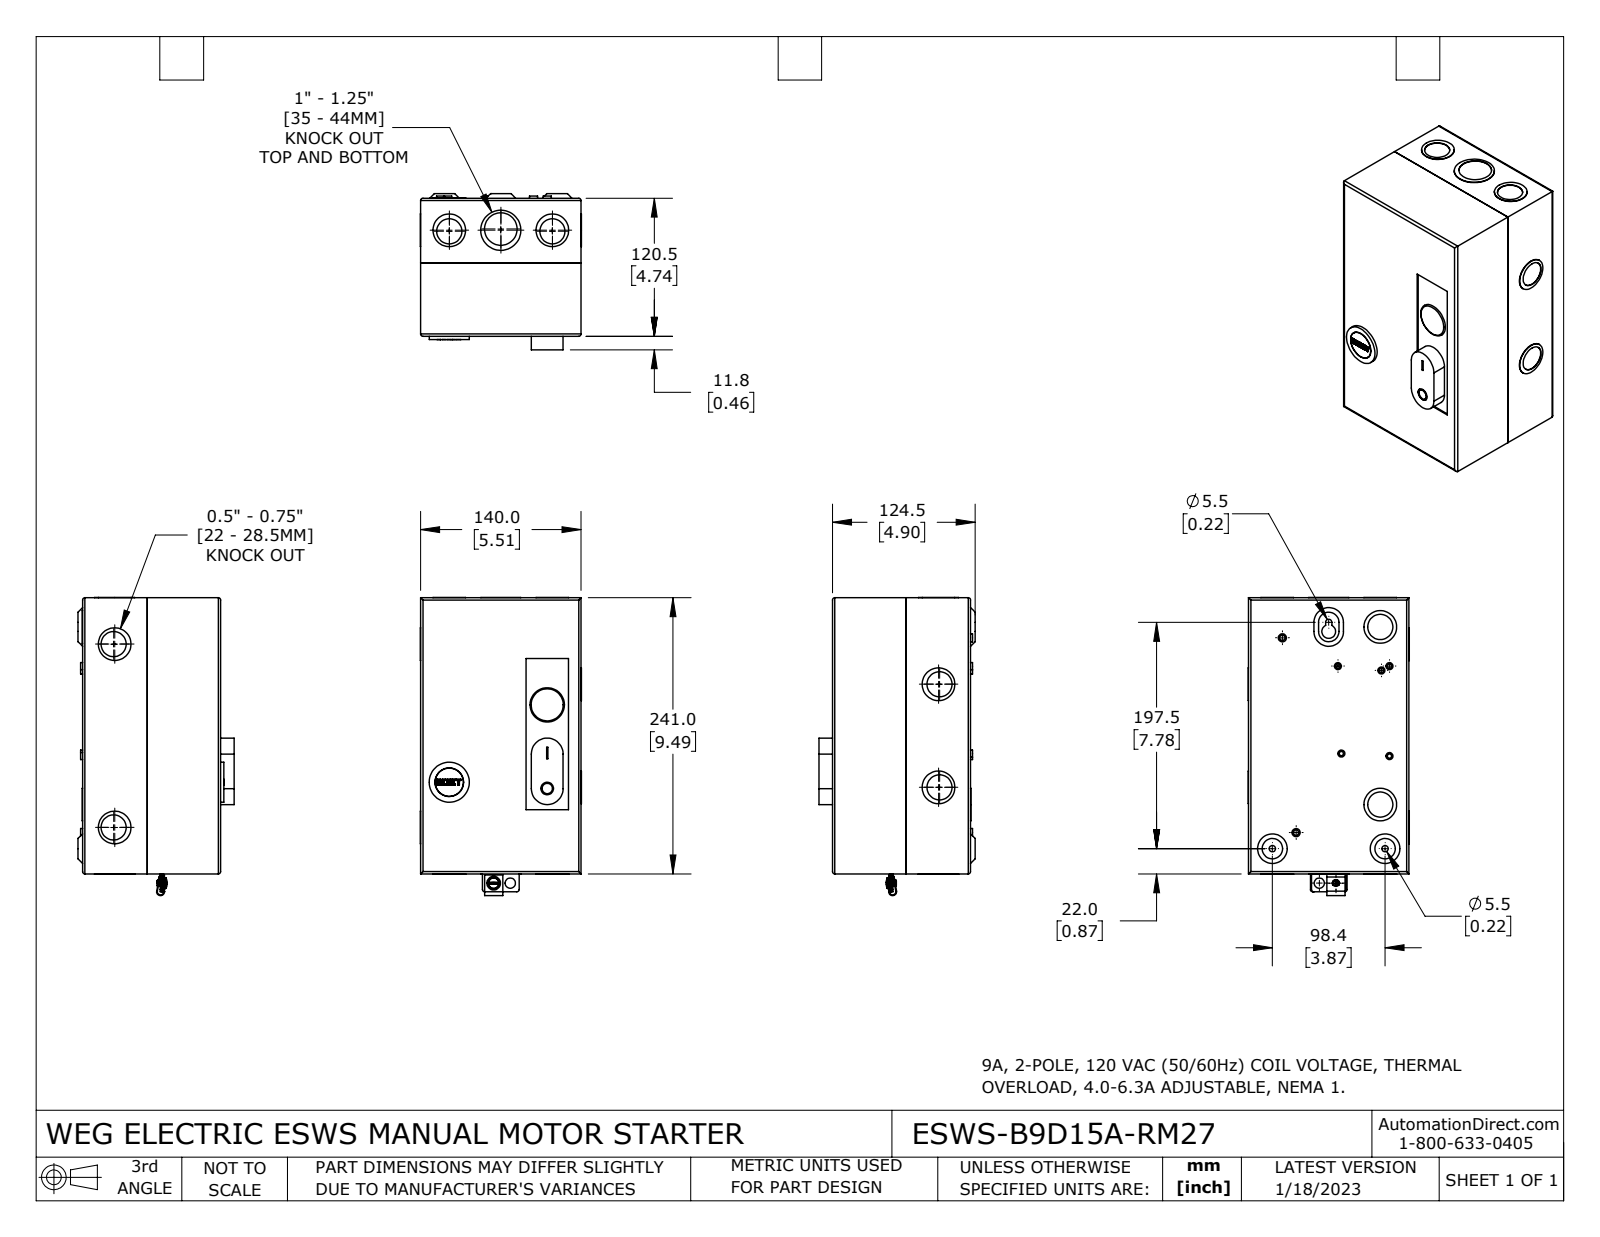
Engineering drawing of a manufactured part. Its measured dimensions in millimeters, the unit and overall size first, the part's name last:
Units: millimetres
Overall size (bounding box): 260.3 × 140.6 × 136.3
Round holes (diameter × count): ⌀3.7 ×5, ⌀21.9 ×4, ⌀4.6 ×2, ⌀5.5 ×2, ⌀9 ×2, ⌀21.9 ×2, ⌀22 ×2, ⌀22.5 ×2, ⌀6.5 ×1, ⌀7.7 ×1, ⌀11 ×1, ⌀11.9 ×1
Round bosses / shafts (diameter × count): ⌀28.5 ×6, ⌀6.1 ×5, ⌀28.5 ×2, ⌀7.1 ×2, ⌀35.1 ×1, ⌀35 ×1, ⌀30.3 ×1, ⌀29.2 ×1
Partial cylindrical surfaces — rounded edges, fillets, slot ends (radius × count): R0.1 ×34, R2 ×13, R0.8 ×4, R2.7 ×3, R1.5 ×2, R1.9 ×2, R3.1 ×2, R3.5 ×2
Main face-to-face distances: 1.2, 119.3, 138.8, 118.1, 239.8, 120.5, 137.6, 140, 1.8, 1.6
Hole centre spacings: 14.5, 35, 45, 86, 90, 125, 152.3, 190.1
Volume: 266 000 mm³ · Surface area: 377 500 mm²
Bodies: 7 solids, 435 faces (168 planar, 230 cylindrical, 37 other)
Part name (STEP PRODUCT): ESWS-B9D15A-RM27
STEP written by: SolidWorks 2021 (CONFIG_CONTROL_DESIGN)
